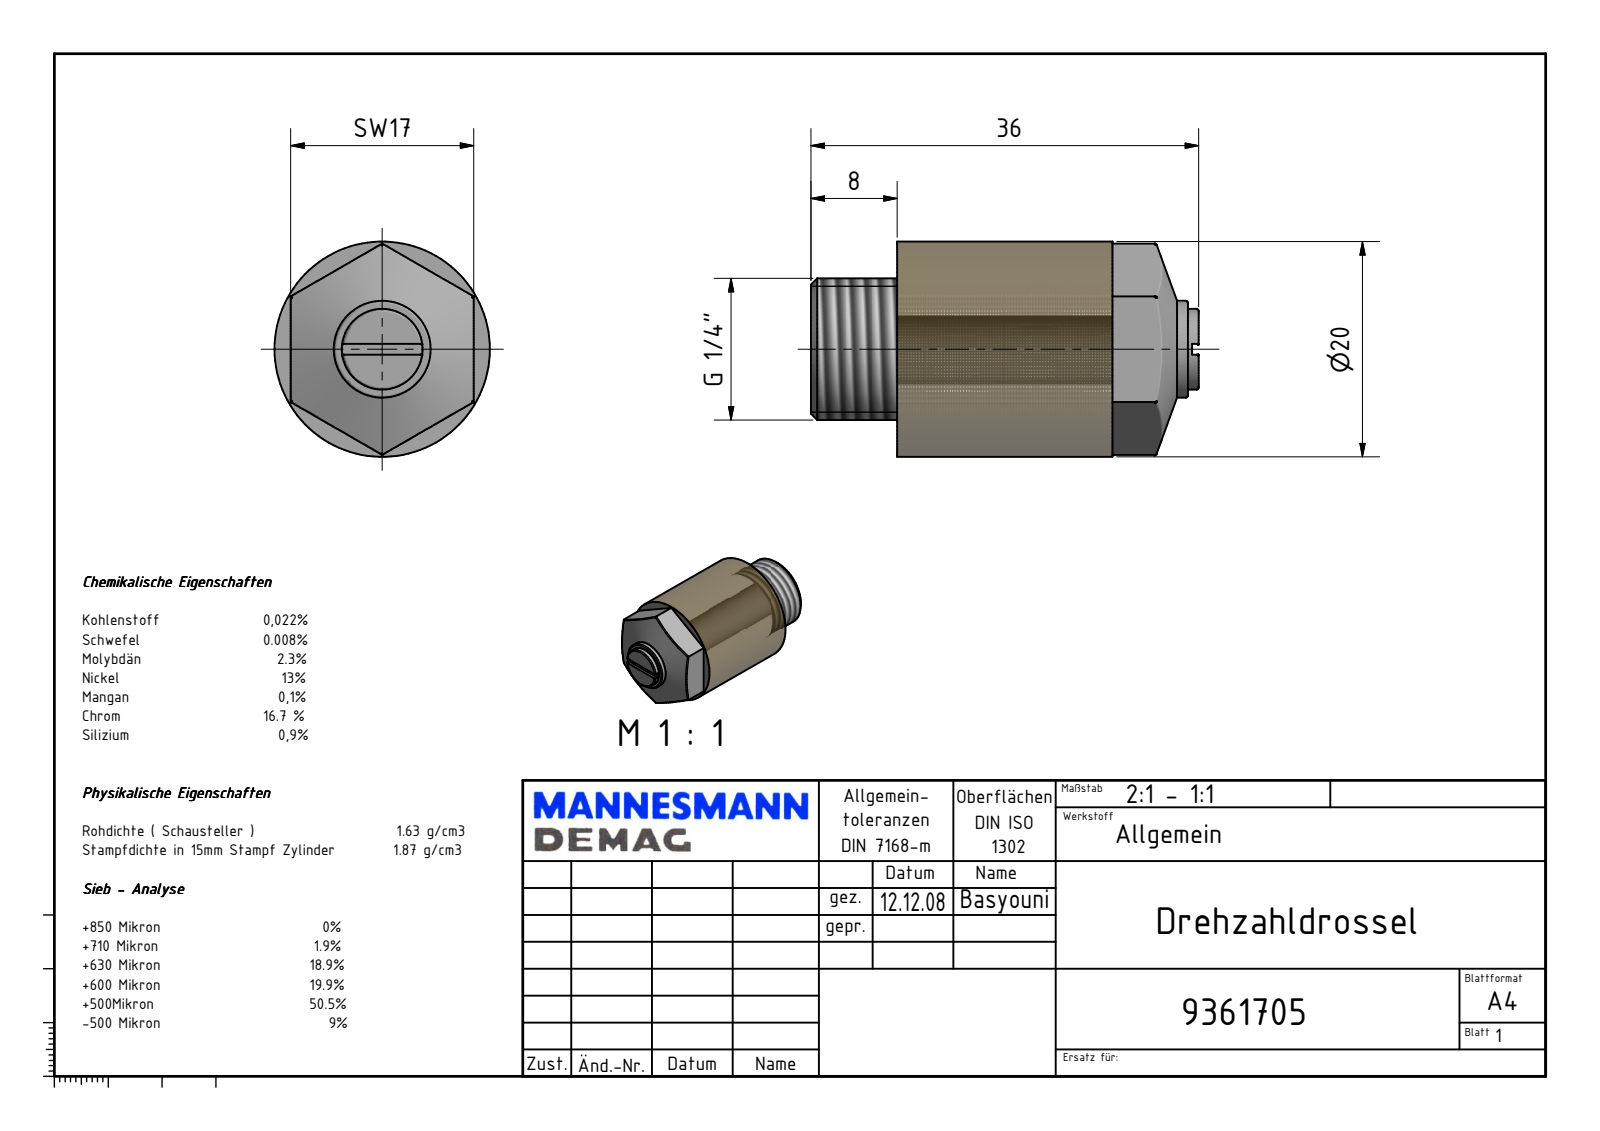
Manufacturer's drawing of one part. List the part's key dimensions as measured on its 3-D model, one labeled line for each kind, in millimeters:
Part name (STEP PRODUCT): 9361705
STEP written by: Autodesk Inventor 2014 (AUTOMOTIVE_DESIGN)
Units: millimetres
Bodies: 1 solid, 33 faces (16 planar, 5 cylindrical, 12 other)
Overall size (bounding box): 36 × 20 × 20
Volume: 7 655 mm³ · Surface area: 3 209 mm²
Round holes (diameter × count): ⌀6.5 ×1
Round bosses / shafts (diameter × count): ⌀20 ×1, ⌀13.16 ×1, ⌀9 ×1, ⌀7.5 ×1
Main face-to-face distances: 17, 8, 28, 20, 6, 26, 34, 2, 36, 1
